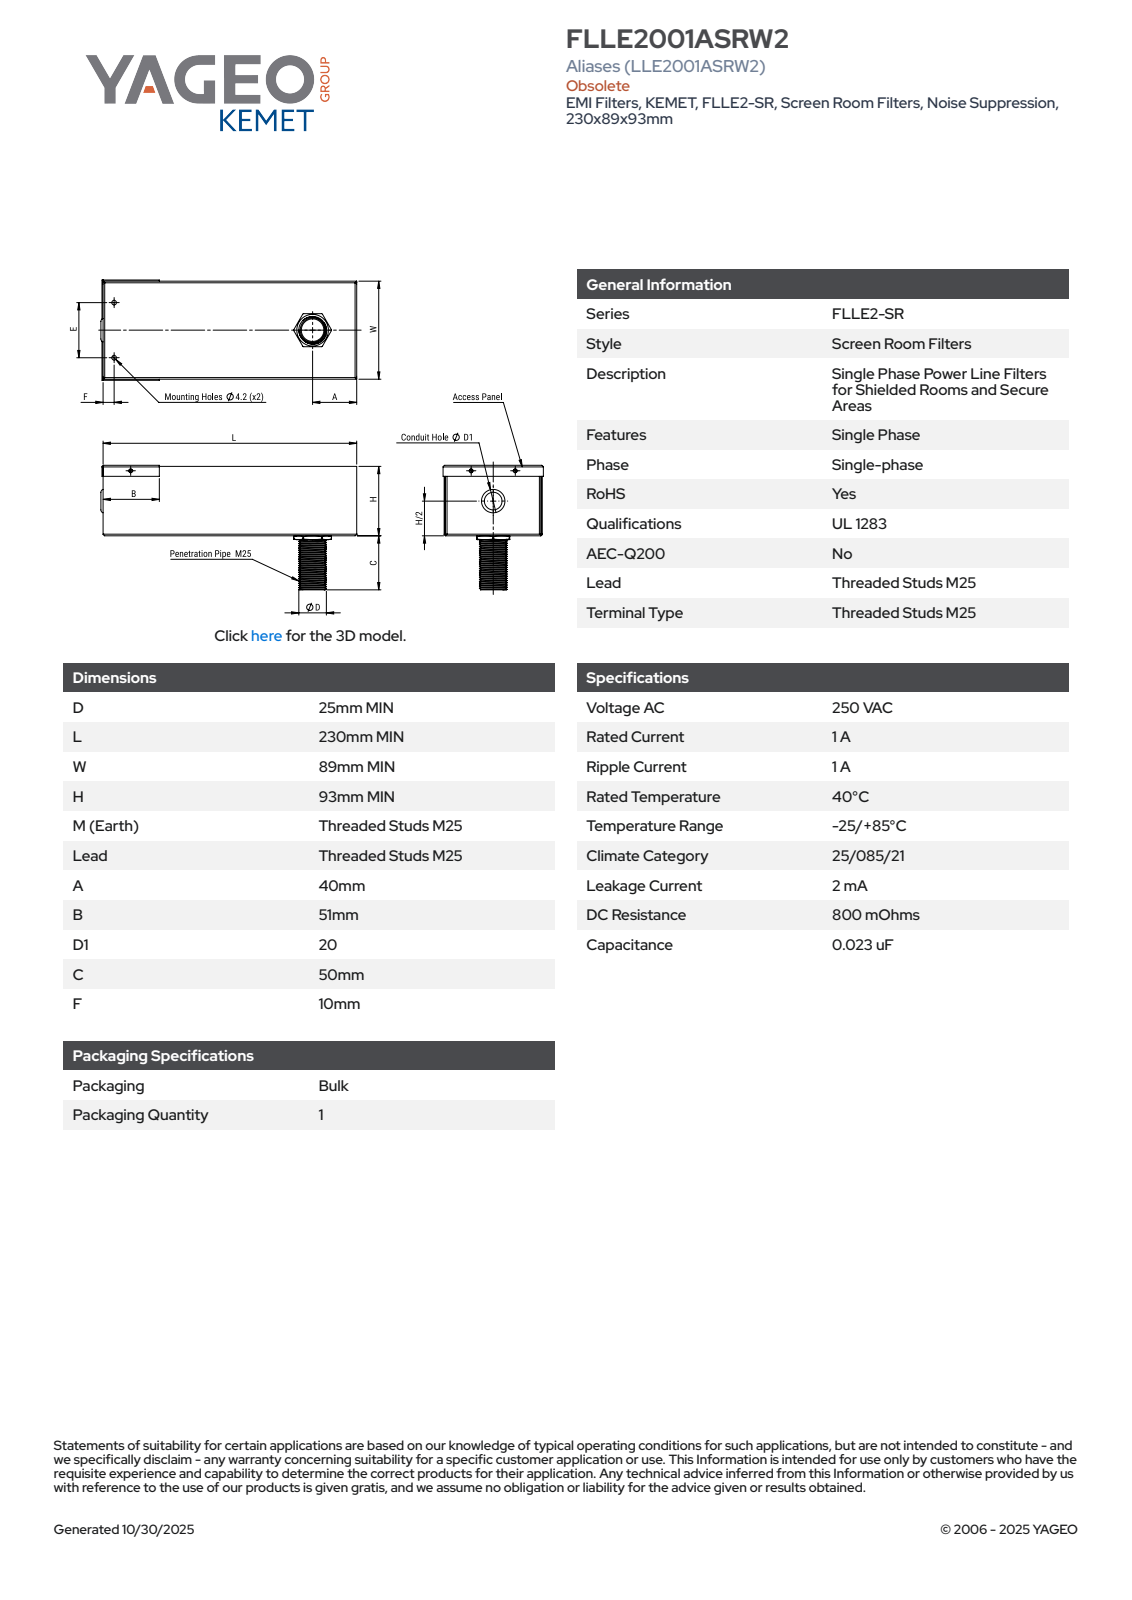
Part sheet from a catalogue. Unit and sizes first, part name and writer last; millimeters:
Units: millimetres
Overall size (bounding box): 234.11 × 113 × 97.22
Round holes (diameter × count): ⌀2.9 ×3, ⌀3.5 ×3, ⌀4.2 ×3, ⌀10.2 ×2, ⌀16 ×1, ⌀20 ×1, ⌀20.5 ×1, ⌀23.9 ×1
Round bosses / shafts (diameter × count): ⌀8 ×3, ⌀4 ×3, ⌀3.09 ×3, ⌀25 ×1, ⌀19 ×1
Partial cylindrical surfaces — rounded edges, fillets, slot ends (radius × count): R0.5 ×16, R1.5 ×16, R1 ×6, R0.74 ×2, R1.74 ×2
Main face-to-face distances: 1, 62, 88, 63, 87, 89, 61, 229, 179, 50
Hole centre spacings: 18, 20, 22.14, 26.91, 34, 40, 43.86, 181.73
Volume: 99 821 mm³ · Surface area: 198 677 mm²
Bodies: 11 solids, 663 faces (232 planar, 314 cylindrical, 117 other)
Part name (STEP PRODUCT): MRX M4x6_92000A216; GEH0414_Case; GEH0414_Lid2; GEH0414_Lid1 (+6 more)
STEP written by: SolidWorks 2021 (AUTOMOTIVE_DESIGN)
